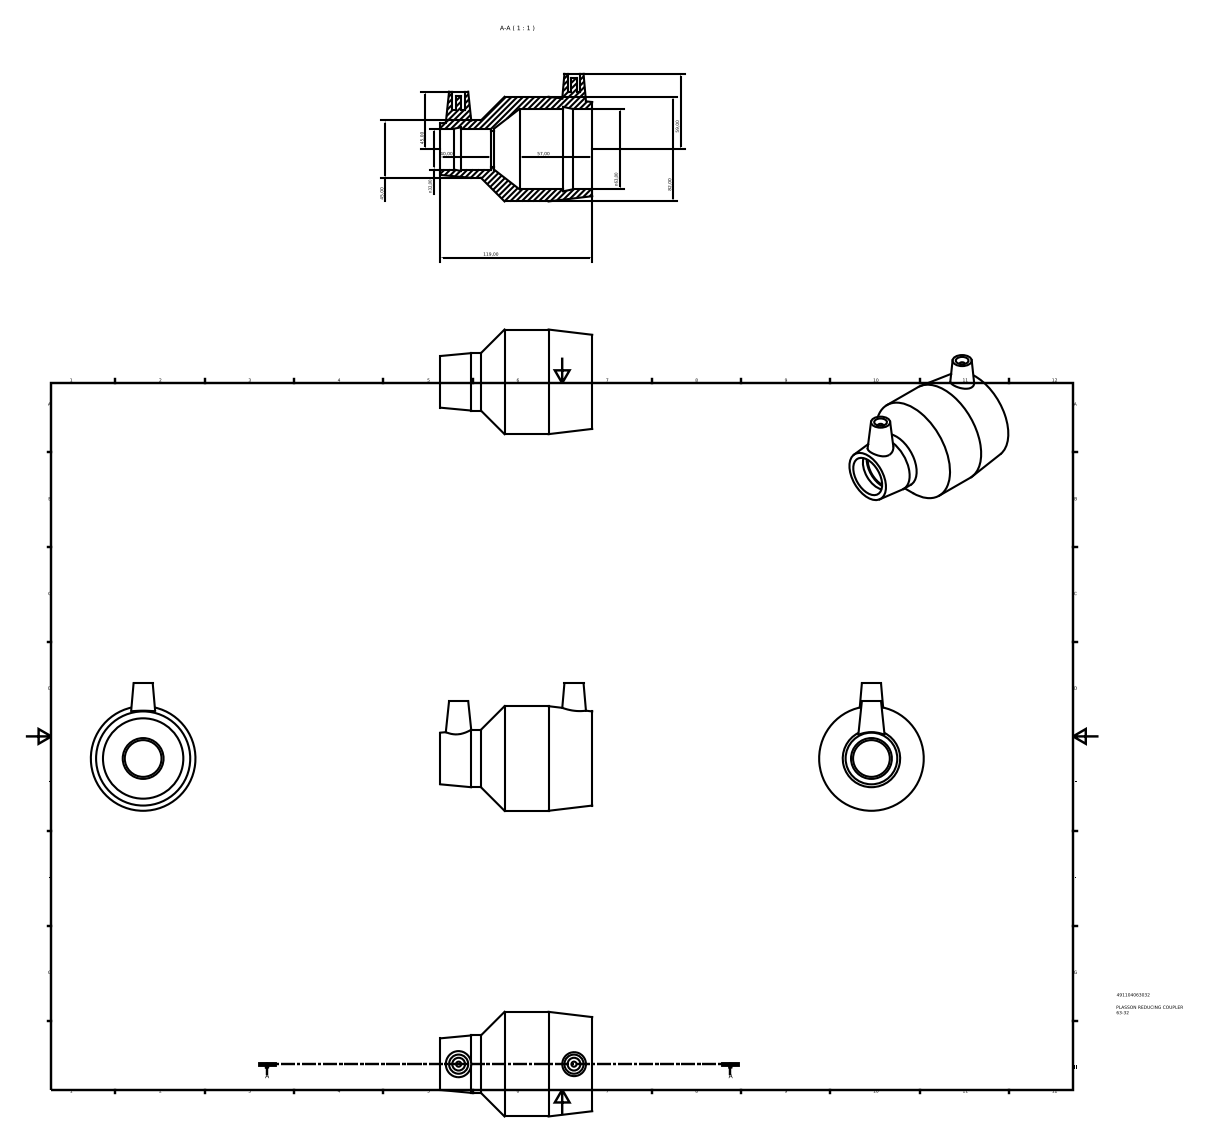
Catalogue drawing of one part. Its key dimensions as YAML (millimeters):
part_name: "491104063032"
step_written_by: "Autodesk Inventor 2015 (AUTOMOTIVE_DESIGN)"
units: millimeters
bodies: {solids: 1, faces: 32, planar: 12, cylindrical: 11, other: 9}
overall_size: [119, 100, 82]
volume: 211784
surface_area: 52028
round_holes:
  - {diameter: 10, count: 2}
  - {diameter: 28.8, count: 1}
  - {diameter: 32, count: 1}
  - {diameter: 63, count: 1}
round_bosses_or_shafts:
  - {diameter: 4, count: 2}
  - {diameter: 82, count: 1}
  - {diameter: 45, count: 1}
face_to_face_distances: [119, 96.2, 22.8, 14, 42, 54.2, 77, 40, 2, 56.2]
hole_center_spacings: [90.44]
